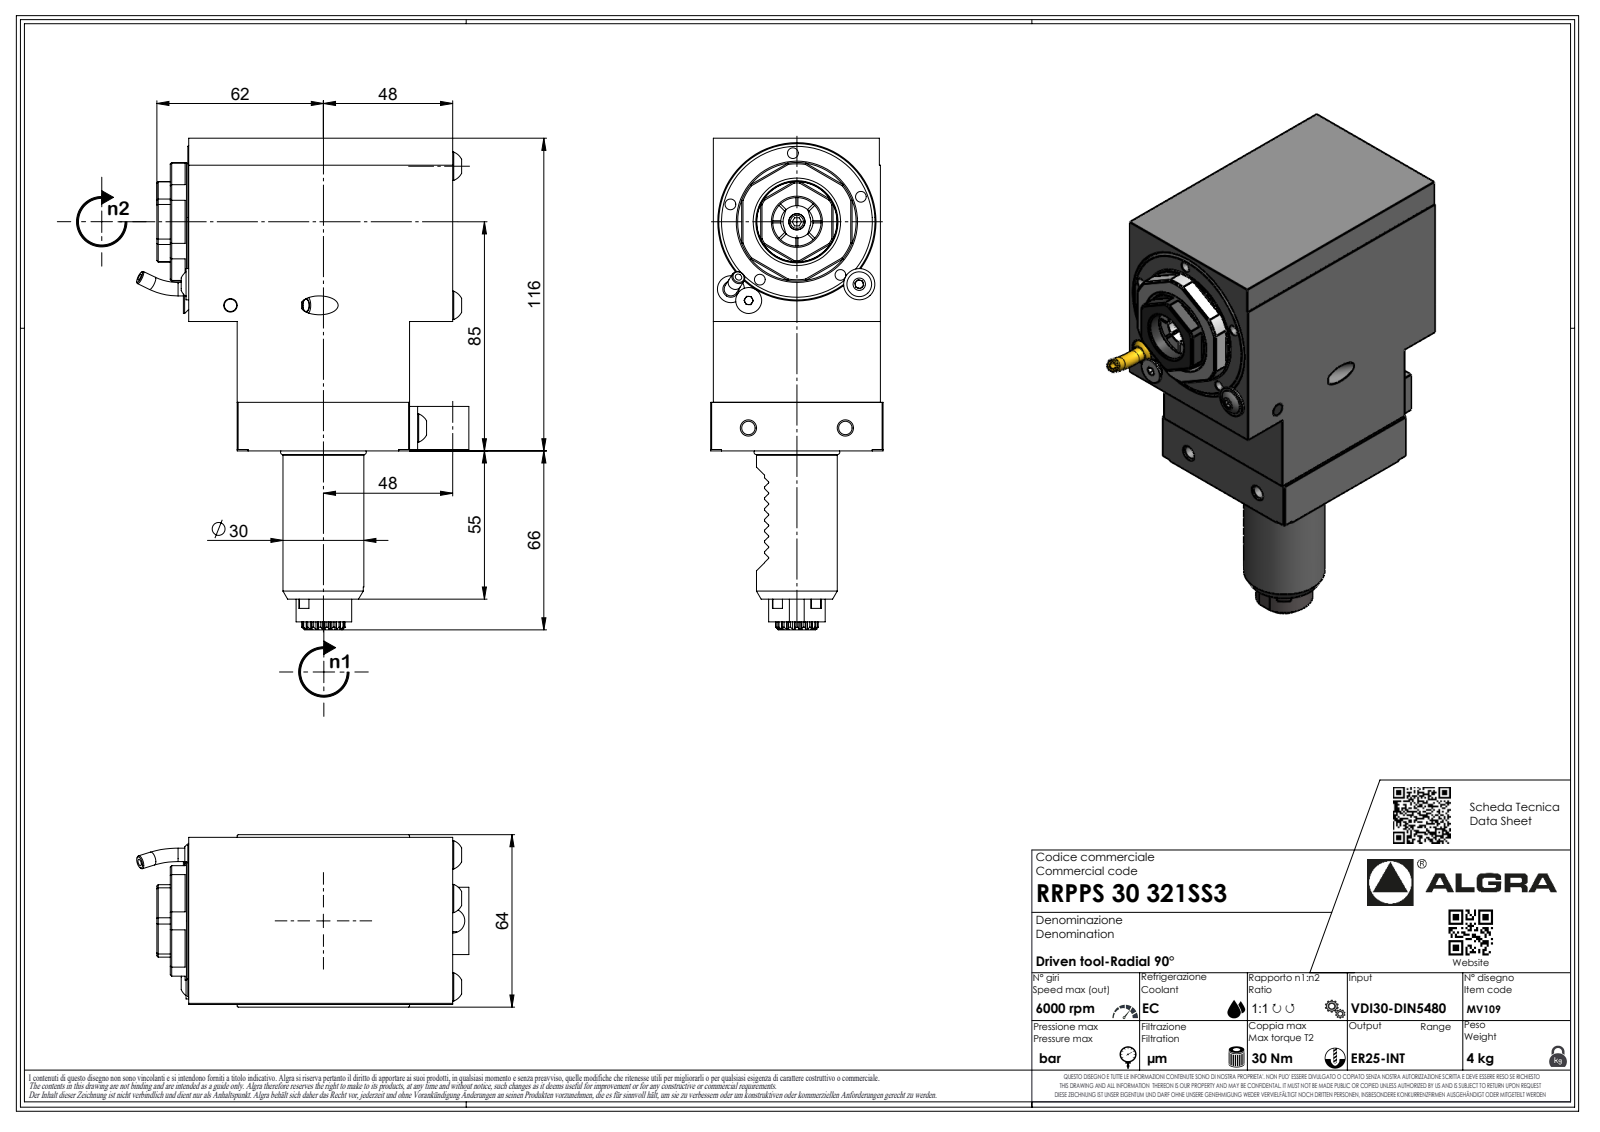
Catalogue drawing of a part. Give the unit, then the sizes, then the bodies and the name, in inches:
Units: inches
Overall size (bounding box): 7.181 × 4.854 × 2.52
Round holes (diameter × count): ⌀0.083 ×1, ⌀0.559 ×1, ⌀0.866 ×1, ⌀1.039 ×1
Round bosses / shafts (diameter × count): ⌀0.413 ×3, ⌀0.197 ×2, ⌀1.732 ×1, ⌀1.181 ×1, ⌀1.146 ×1, ⌀0.827 ×1, ⌀0.52 ×1, ⌀0.251 ×1
Partial cylindrical surfaces — rounded edges, fillets, slot ends (radius × count): R0.012 ×8, R0.013 ×7, R0.02 ×7, R0.146 ×7, R0.008 ×1, R0.28 ×1, R0.312 ×1, R0.407 ×1
Main face-to-face distances: 2.441, 2.52, 4.567, 3.15, 0.63, 0.039, 2.48, 1.89, 2.677, 0.709
Hole centre spacings: 0.984
Volume: 40.63 in³ · Surface area: 93.37 in²
Bodies: 1 solid, 911 faces (597 planar, 102 cylindrical, 212 other)
Part name (STEP PRODUCT): RRPPS30321SS3
STEP written by: SolidWorks 2023 (AUTOMOTIVE_DESIGN)
